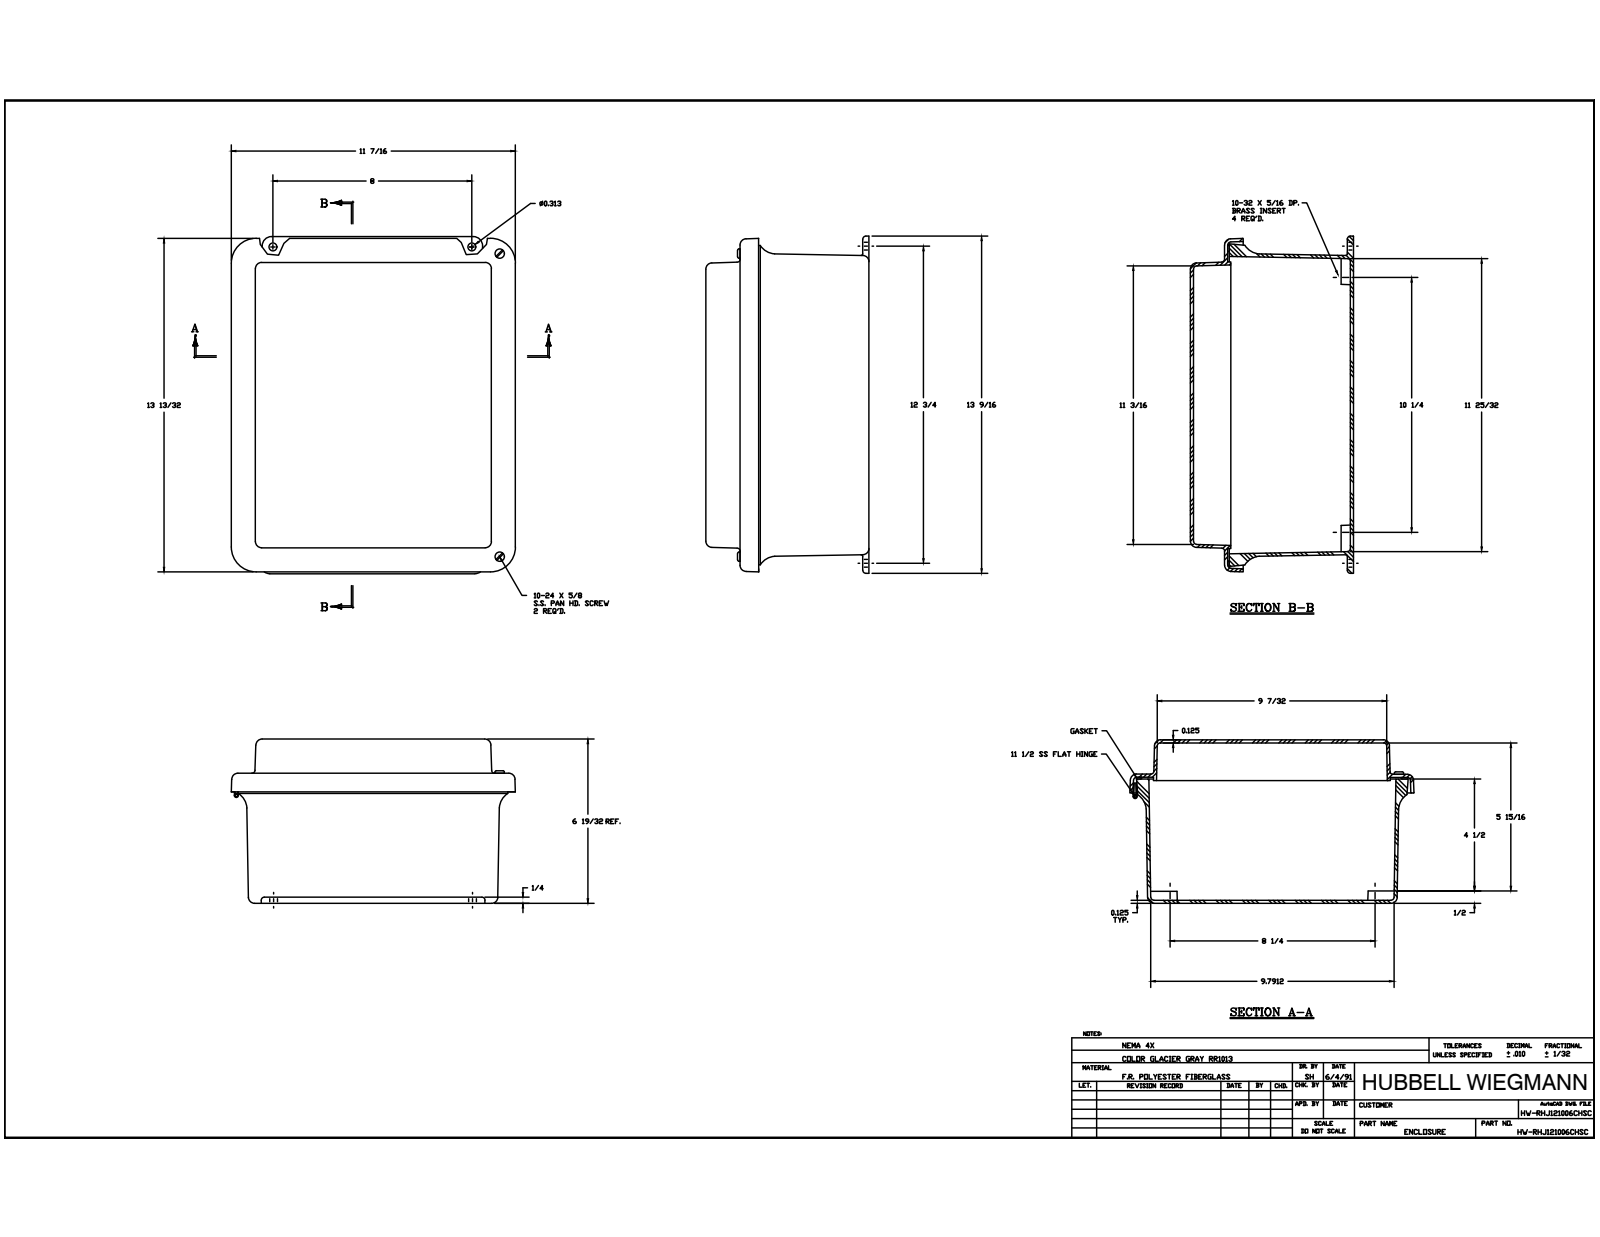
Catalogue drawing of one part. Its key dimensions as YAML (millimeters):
part_name: "J1210HW_3; RMINS45821P_185; RMINS45821P_186; RMINS45821P_187 (+8 more)"
step_written_by: "Autodesk Inventor 2014 (AUTOMOTIVE_DESIGN)"
units: millimeters
bodies: {solids: 22, faces: 858, planar: 306, cylindrical: 323, other: 229}
overall_size: [344.49, 290.94, 167.33]
volume: 1500000
surface_area: 823678
round_holes:
  - {diameter: 3.33, count: 8}
  - {diameter: 3.56, count: 8}
  - {diameter: 3.86, count: 5}
  - {diameter: 3.96, count: 4}
  - {diameter: 5.54, count: 4}
  - {diameter: 3.68, count: 2}
  - {diameter: 2.16, count: 1}
  - {diameter: 2.16, count: 1}
round_bosses_or_shafts:
  - {diameter: 6.35, count: 8}
  - {diameter: 3.17, count: 8}
  - {diameter: 6.86, count: 6}
  - {diameter: 4.83, count: 2}
  - {diameter: 3.97, count: 2}
  - {diameter: 3.94, count: 1}
partial_cylinders:
  - {radius: 0.79, count: 20}
  - {radius: 3.17, count: 20}
  - {radius: 6.35, count: 12}
  - {radius: 5.08, count: 4}
  - {radius: 7.24, count: 4}
  - {radius: 7.94, count: 4}
  - {radius: 9.53, count: 4}
  - {radius: 19.05, count: 4}
face_to_face_distances: [3.18, 164.15, 167.33, 160.97, 128.92, 35.23, 125.74, 38.41, 132.1, 32.05]
hole_center_spacings: [92.08, 34.24, 235, 285.58, 368.25, 6.35, 92.07, 174.62]
